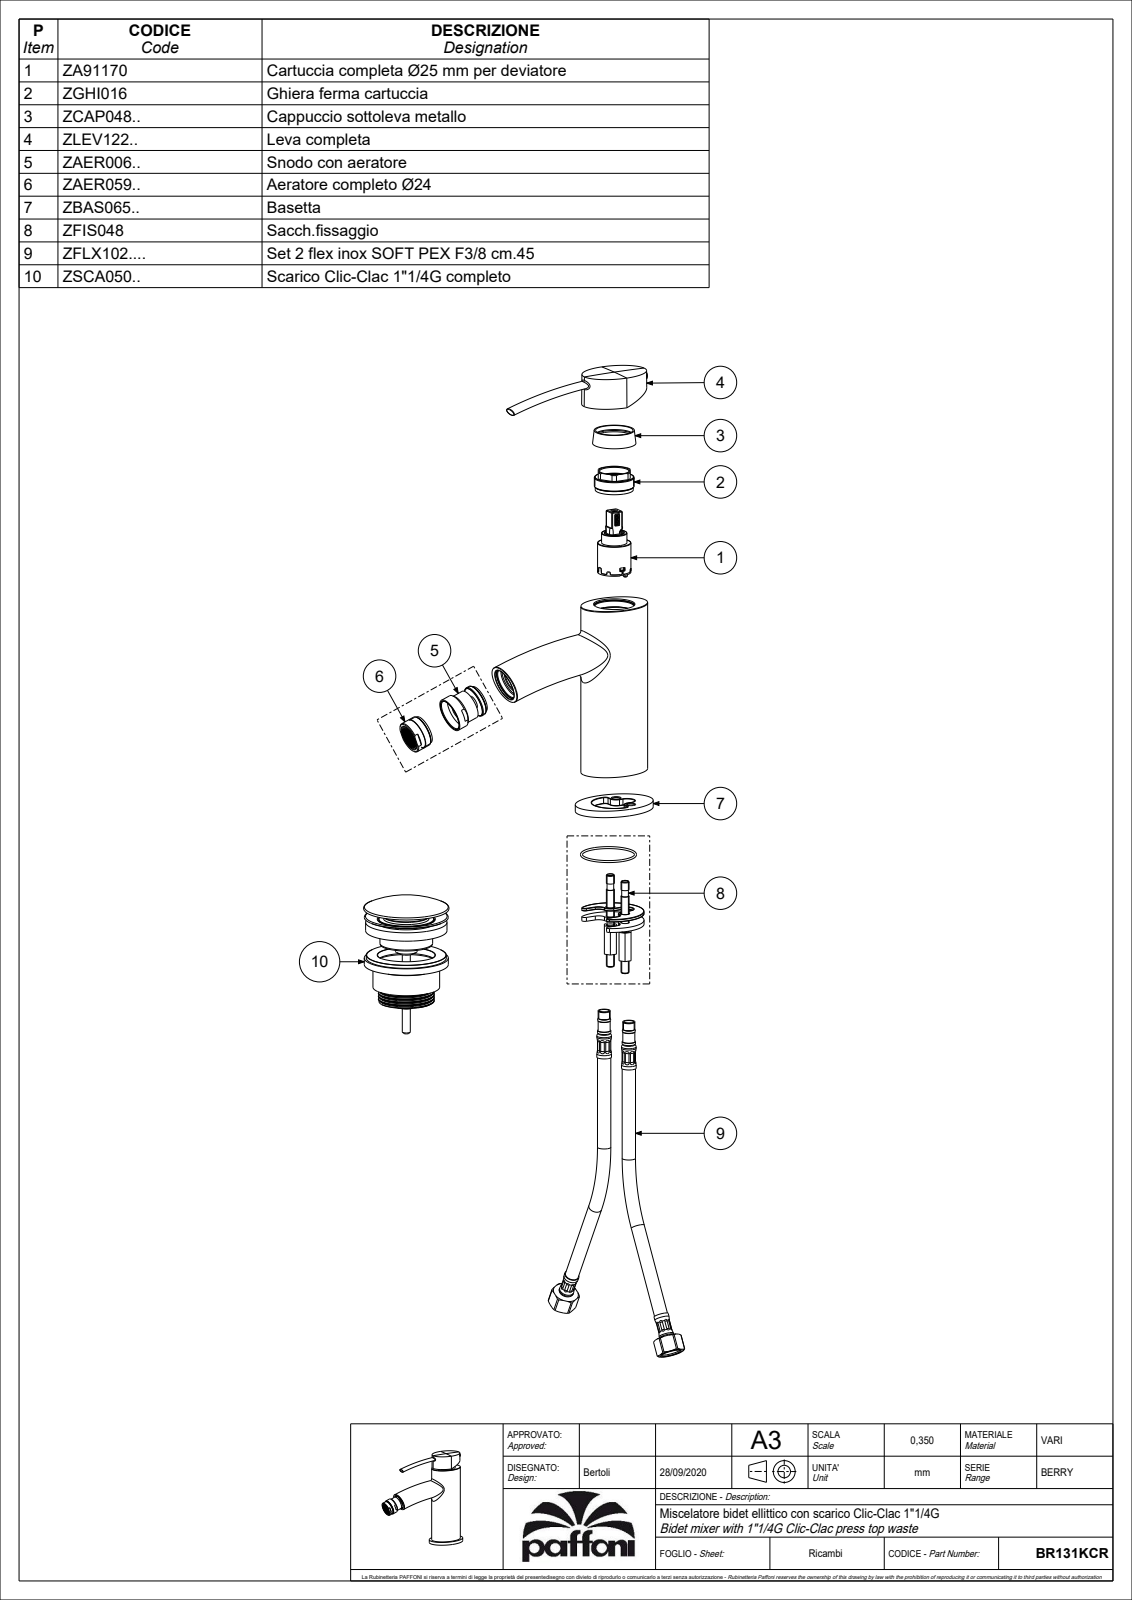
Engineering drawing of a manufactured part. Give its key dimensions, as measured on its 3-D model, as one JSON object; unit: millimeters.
{"part_name": "BR131CR", "step_written_by": "CREO PARAMETRIC BY PTC INC, 2020044 (CONFIG_CONTROL_DESIGN)", "units": "millimeters", "bodies": {"solids": 5, "faces": 2776, "planar": 1986, "cylindrical": 417, "other": 373}, "overall_size": [159.2, 156.31, 46], "volume_mm3": 164071, "surface_area_mm2": 98279, "round_holes": [[4.5, 3], [7, 3], [3, 2], [5, 2], [5.5, 2], [6.2, 2], [6.5, 2], [9.4, 2], [16, 2], [20, 2], [5.3, 1], [8, 1]], "round_bosses_or_shafts": [[10, 3], [5, 3], [11, 2], [9, 2], [6, 2], [38.8, 1], [28.7, 1], [28.5, 1]], "partial_cylinders_radius": [[0.5, 40], [3, 29], [0.3, 23], [1, 18], [0.2, 13], [0.15, 10], [2, 10], [1.5, 8]], "face_to_face_distances": [5, 90.5, 156.9, 102.5, 12, 22.9, 151.9, 1.5, 7, 6], "hole_center_spacings": [7.5, 11, 11.24, 11.4, 13.46, 13.6, 13.87, 21.1]}
